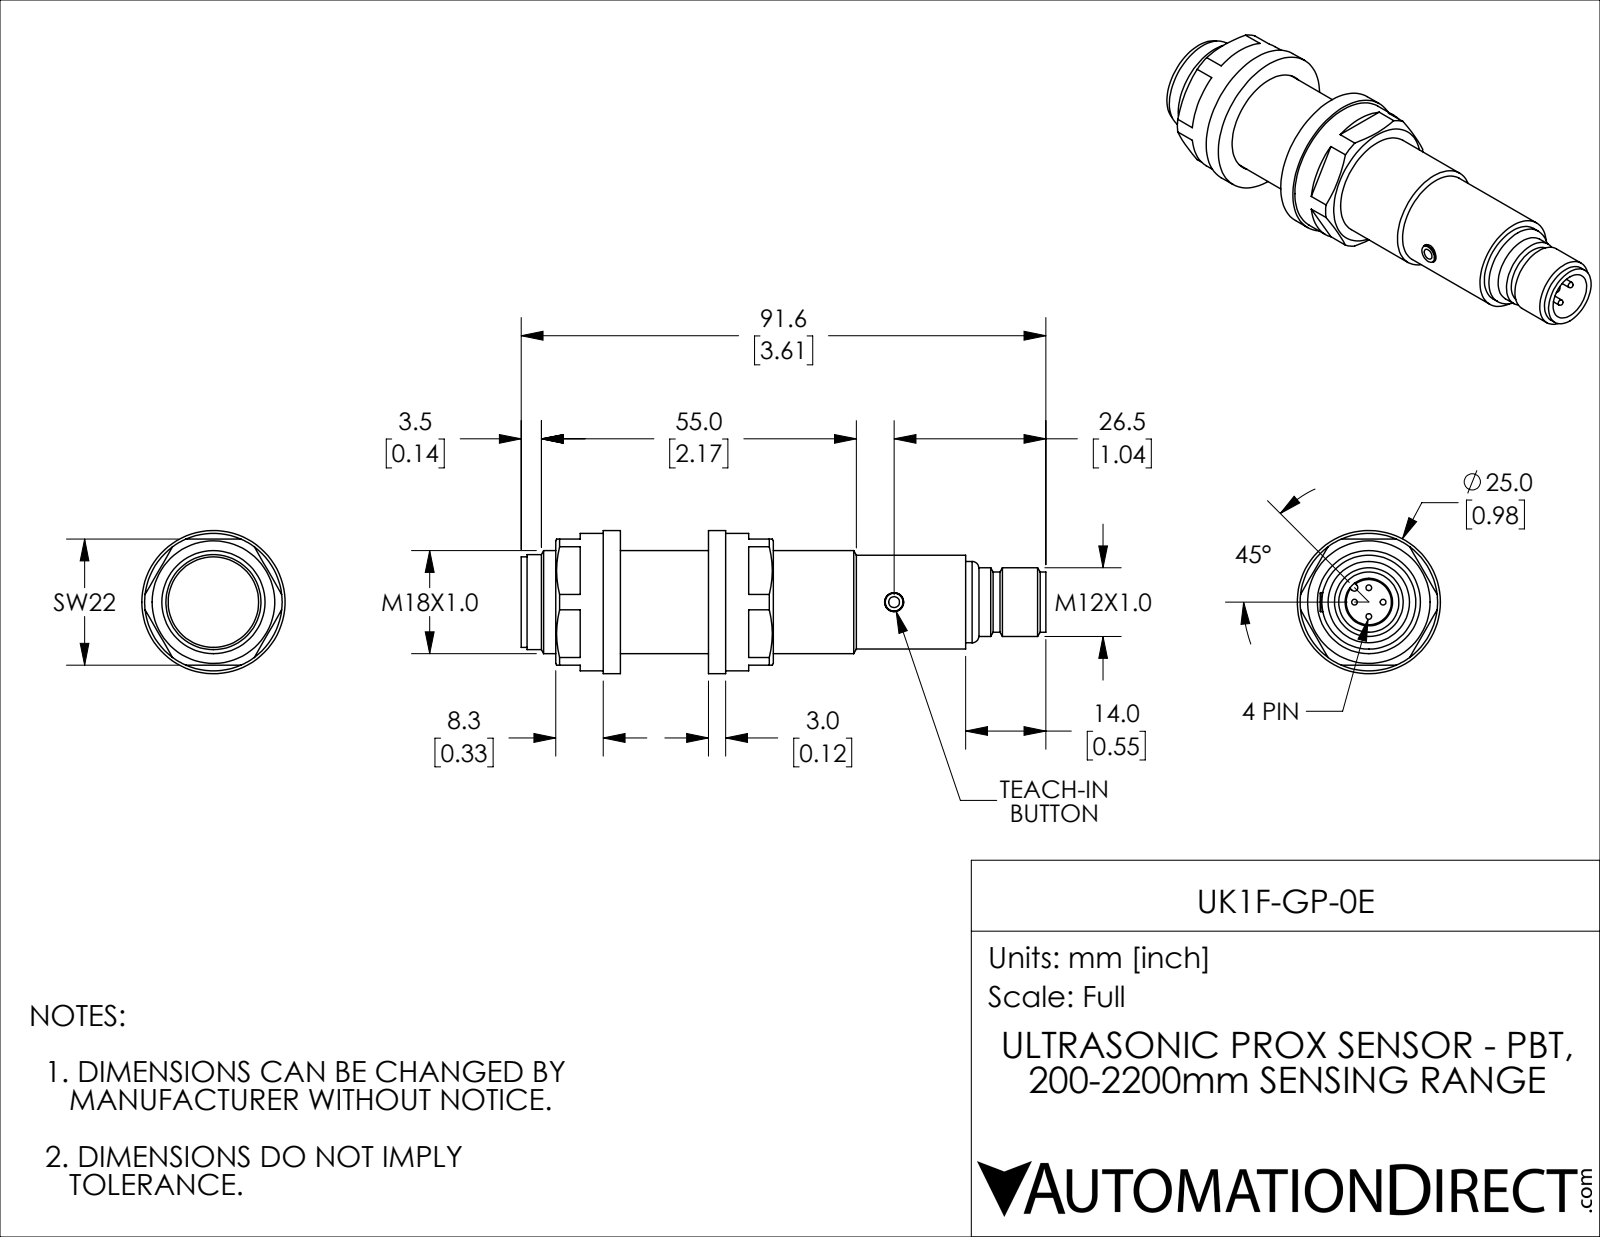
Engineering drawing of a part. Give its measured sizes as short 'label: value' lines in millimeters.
name: UK1F-GP-0E
written by: SolidWorks 2018 (AUTOMOTIVE_DESIGN)
unit: mm
bodies: 6 solids, 123 faces (43 planar, 49 cylindrical, 31 other)
size: 91.6 × 25 × 25
volume: 24 200 mm³; area: 10 330 mm²
holes: 1× ⌀3.3, 1× ⌀8.3, 1× ⌀18, 1× ⌀18.2
bosses: 4× ⌀1, 1× ⌀25, 1× ⌀24, 1× ⌀16.6, 1× ⌀16.4, 1× ⌀15.8, 1× ⌀14.2, 1× ⌀12
rounds: 1× R0.6
face distances: 3, 18.4, 21.4, 15.4, 22, 8.3, 11.3, 26.7, 29.7, 14.3
